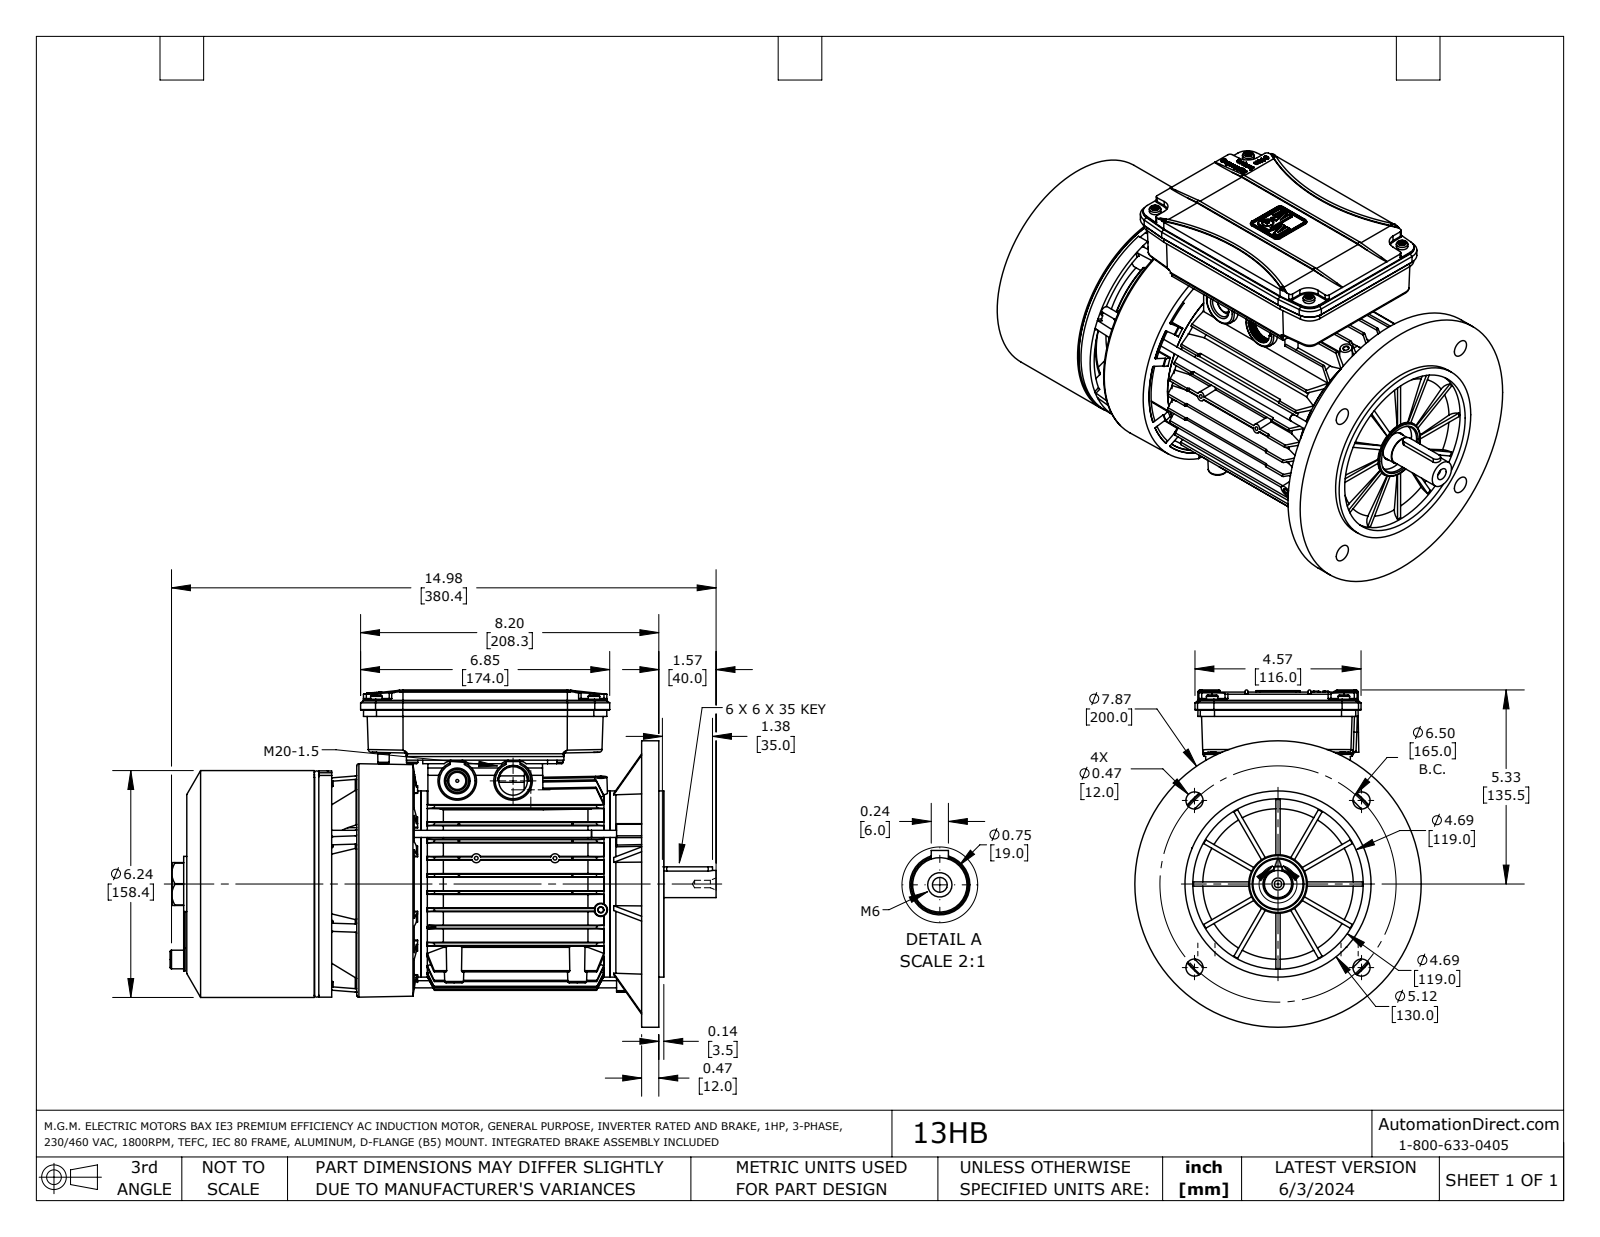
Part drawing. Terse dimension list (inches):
name: 13HB
written by: SolidWorks 2021 (AUTOMOTIVE_DESIGN)
unit: in
bodies: 22 solids, 3691 faces (1359 planar, 1030 cylindrical, 1302 other)
size: 15.015 × 9.272 × 7.874
volume: 91.27 in³; area: 1 329 in²
holes: 14× ⌀0.13, 12× ⌀0.177, 11× ⌀0.236, 8× ⌀0.146, 8× ⌀0.157, 8× ⌀0.217, 7× ⌀0.098, 5× ⌀0.472, 4× ⌀0.118, 3× ⌀0.165, 3× ⌀0.276, 1× ⌀0.205
bosses: 8× ⌀0.177, 8× ⌀0.118, 4× ⌀0.315, 3× ⌀0.197, 2× ⌀1.063, 2× ⌀0.248, 1× ⌀7.874, 1× ⌀6.339
rounds: 80× R0.039, 56× R0.02, 35× R0.079, 32× R0.008, 30× R0.035, 24× R0.012, 16× R0.004, 16× R0.087
face distances: 0.079, 0.354, 0.217, 12.98, 12.933, 0.047, 0.236, 0.078, 0.433, 0.256
hole spacings: 2.796, 0.472, 2.359, 2.756, 3.252, 3.159, 3.272, 0.473
